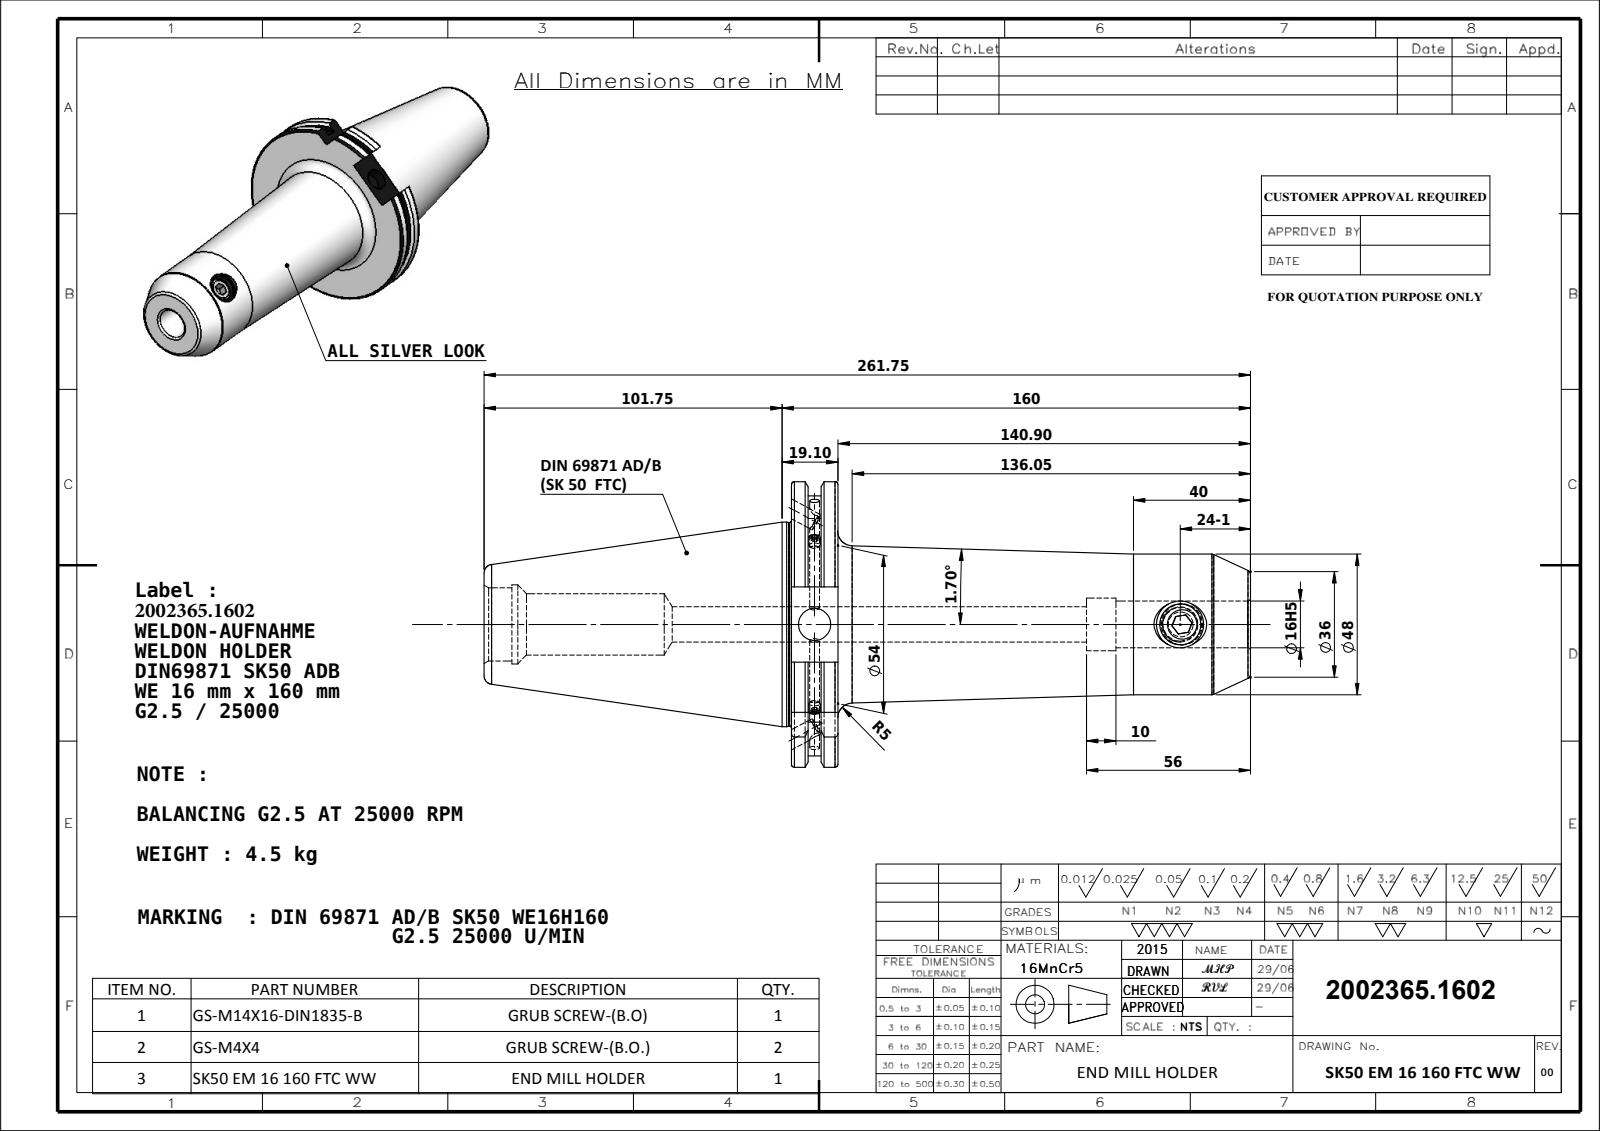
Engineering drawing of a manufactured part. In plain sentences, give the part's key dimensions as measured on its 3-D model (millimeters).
The part is named "SK50 EM 16 160 FTC WW; M14X16_ISO 4026 - M12 x 12-N; 91506-WE716160; M4X4_DIN 913 - M4 x 4-N". Its 3-D file was written by "SolidWorks 2009 (CONFIG_CONTROL_DESIGN)". It is 4 solids with 170 faces: 53 planar, 55 cylindrical and 62 other. Overall it measures 261.75 by 97.5 by 94.05 millimeters. Its volume is 583 940 cubic millimeters and its surface area 71 898 square millimeters. Round holes: 2 of diameter 6, 2 of diameter 12, 2 of diameter 16, 1 of diameter 3.3, 1 of diameter 11, 1 of diameter 18, 1 of diameter 21, 1 of diameter 25, 1 of diameter 27. Round bosses or shafts: 2 of diameter 4, 1 of diameter 69.85, 1 of diameter 69.45, 1 of diameter 48, 1 of diameter 14. Partial cylindrical surfaces (rounded edges, fillets, slot ends): 1 of radius 44.9, 1 of radius 48.75. The main face-to-face distances are 15.9, 156.8, 140.9, 5.66, 10.24, 151.14, 10.15, 4.49, 5.75, 146.65. The hole center spacings are 124.9.
